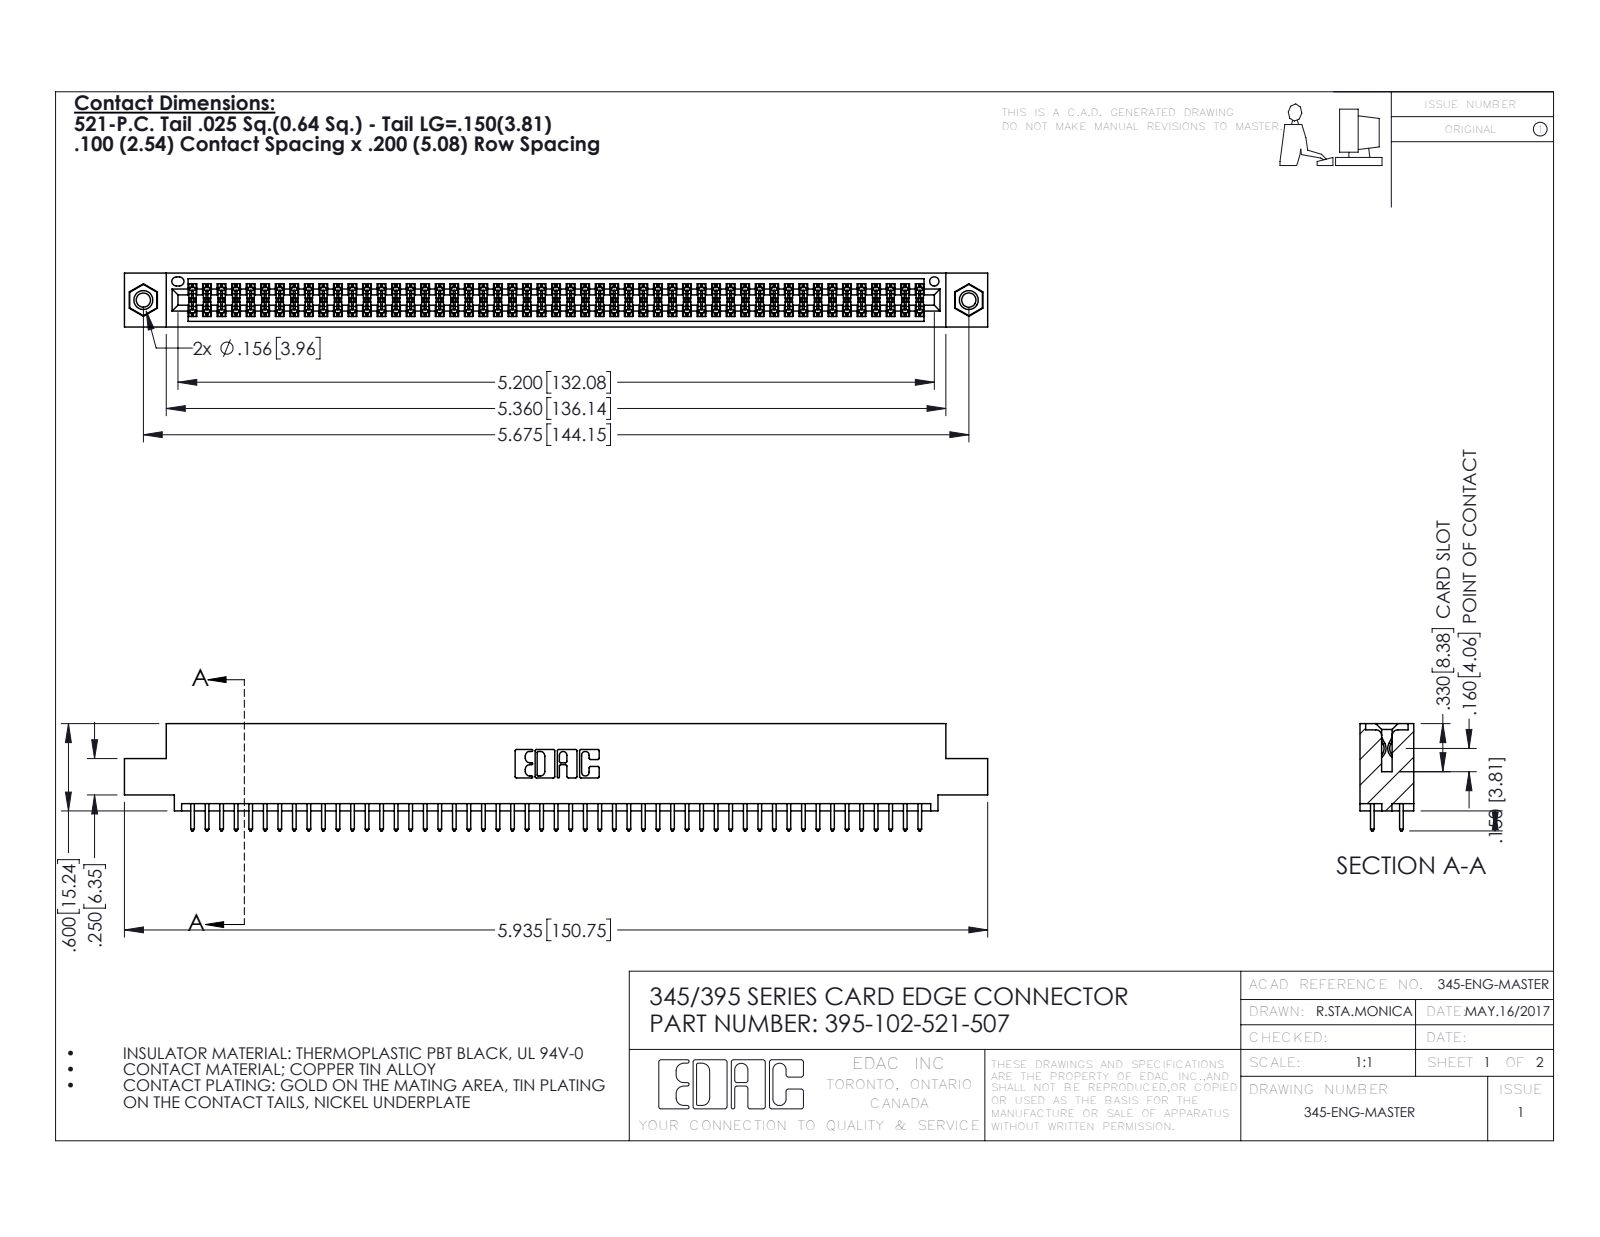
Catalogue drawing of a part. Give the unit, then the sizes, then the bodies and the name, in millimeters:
Units: millimetres
Overall size (bounding box): 150.7 × 18.7 × 9.4
Round holes (diameter × count): ⌀2.5 ×2, ⌀3.2 ×2, ⌀4 ×2, ⌀1.6 ×1
Round bosses / shafts (diameter × count): ⌀3.9 ×2
Partial cylindrical surfaces — rounded edges, fillets, slot ends (radius × count): R0.2 ×153, R0.3 ×102, R0.3 ×22, R0.2 ×6, R0.8 ×6, R0.7 ×3, R0.4 ×2, R0.5 ×2
Main face-to-face distances: 1.8, 7.6, 5.1, 9.4, 2.5, 6.9, 0.6, 5.7, 4.4, 3.8
Hole centre spacings: 6.9, 138.2, 144.1
Volume: 14 600 mm³ · Surface area: 21 610 mm²
Bodies: 105 solids, 5290 faces (3482 planar, 1792 cylindrical, 16 other)
Part name (STEP PRODUCT): 345-250-001_345-250-005-103; 395-102-521-507; 345 Part_0.110 Offset - 0.156 Dia-TI; 345-292-001_345-293-121
STEP written by: SolidWorks 2016 (CONFIG_CONTROL_DESIGN)
